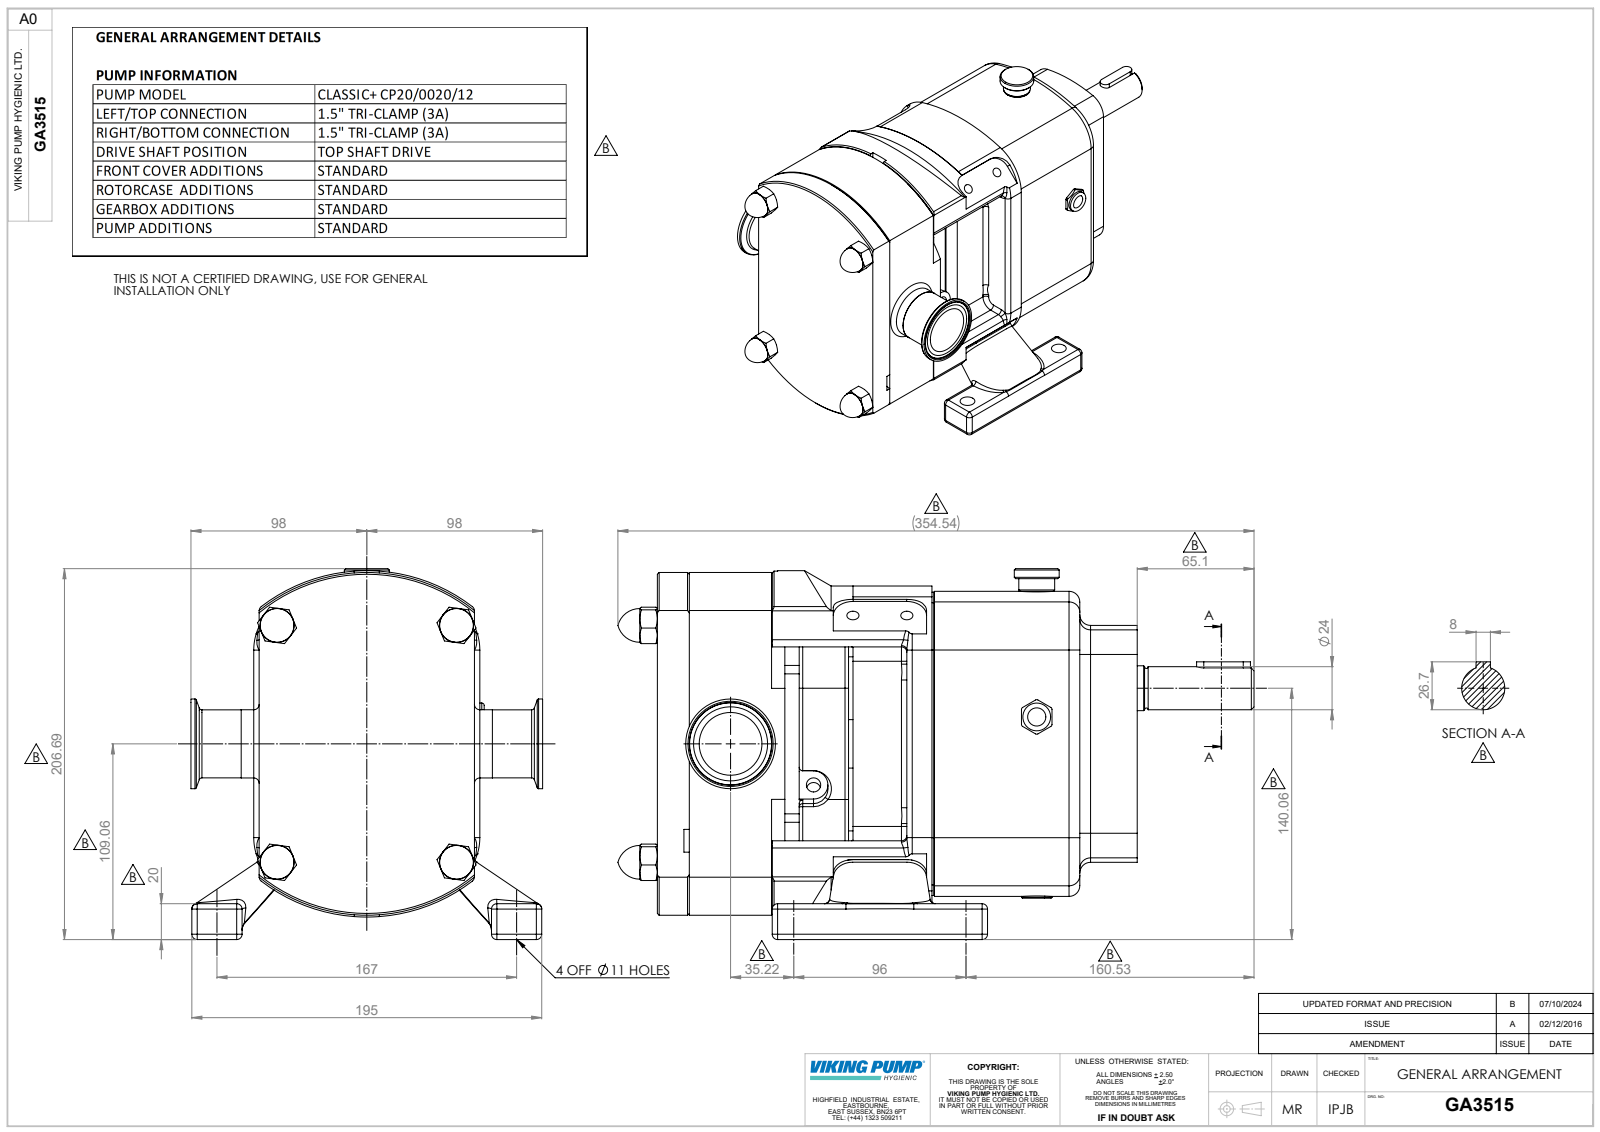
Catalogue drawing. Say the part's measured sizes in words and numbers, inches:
The part is named "Copy (2) of CP20-0020-12 H T^GA3515; Copy of Z94-5121-22 - 1.5 INCH^GA3515; GA3515". Its 3-D file was written by "SolidWorks 2023 (AUTOMOTIVE_DESIGN)". It is 3 solids with 827 faces: 253 planar, 284 cylindrical and 290 other. Overall it measures 13.958 by 8.137 by 7.717 inches. Its volume is 290.2 cubic inches and its surface area 461.8 square inches. Round holes: 4 of diameter 0.268, 4 of diameter 0.433, 3 of diameter 0.255, 2 of diameter 0.315, 1 of diameter 0.887, 1 of diameter 1.378. Round bosses or shafts: 2 of diameter 1.378, 2 of diameter 0.669, 1 of diameter 1.969, 1 of diameter 1.496, 1 of diameter 1.492, 1 of diameter 0.985, 1 of diameter 0.984, 1 of diameter 0.945. Partial cylindrical surfaces (rounded edges, fillets, slot ends): 55 of radius 0.118, 18 of radius 0.079, 16 of radius 0.039, 8 of radius 0.236, 8 of radius 0.437, 6 of radius 0.05, 6 of radius 0.157, 6 of radius 0.315. The main face-to-face distances are 4.724, 4.293, 6.236, 10.529, 0.984, 3.74, 0.798, 3.926, 0.186, 2.942. The hole center spacings are 2.114, 1.183, 3.636, 3.78, 6.576, 2.405, 6.264, 6.264.
